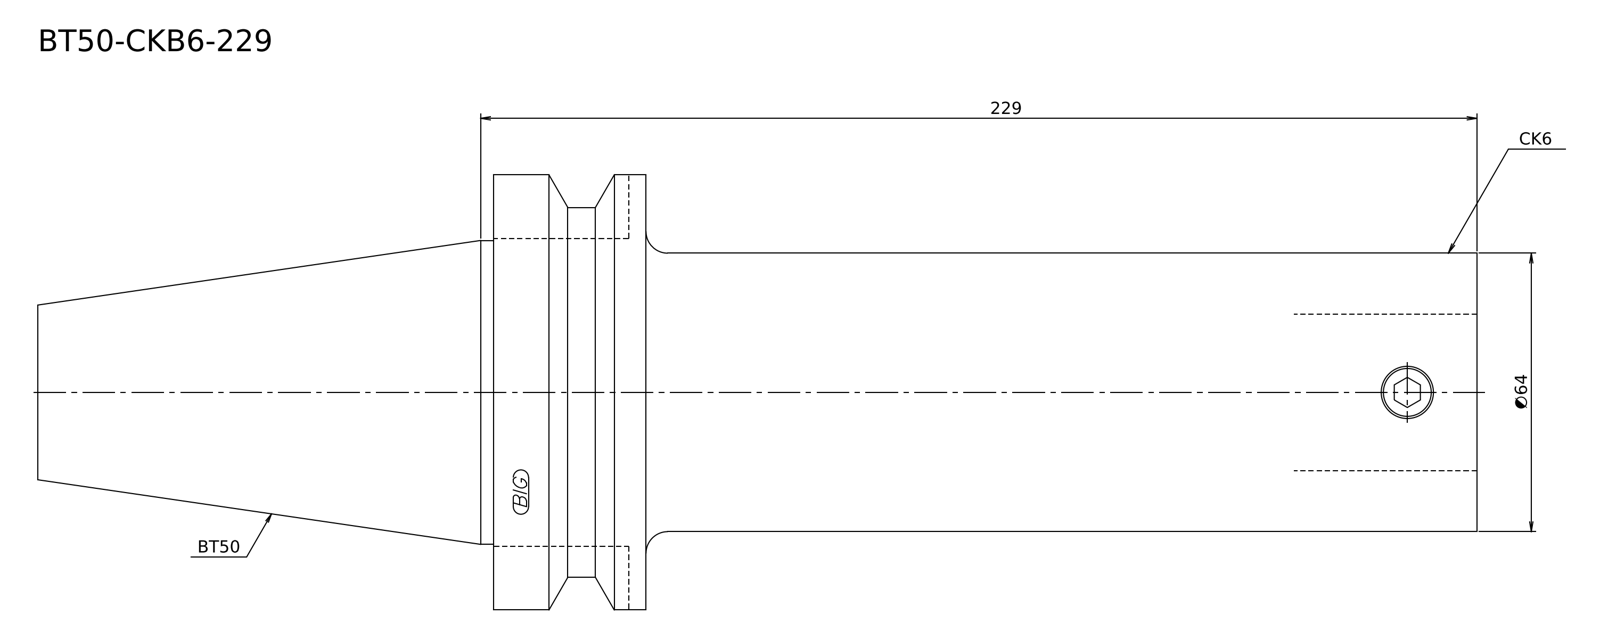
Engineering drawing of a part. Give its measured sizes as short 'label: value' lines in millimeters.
written by: Kubotek KeyCreator V8.5.1 (14335) (CONFIG_CONTROL_DESIGN)
unit: mm
bodies: 1 solid, 13 faces (4 planar, 5 cylindrical, 4 other)
size: 330.8 × 100 × 100
volume: 1 128 000 mm³; area: 82 434 mm²
bosses: 1× ⌀100, 1× ⌀85, 1× ⌀69.85, 1× ⌀64
face distances: 35, 191, 226, 330.8, 139.8, 104.8
